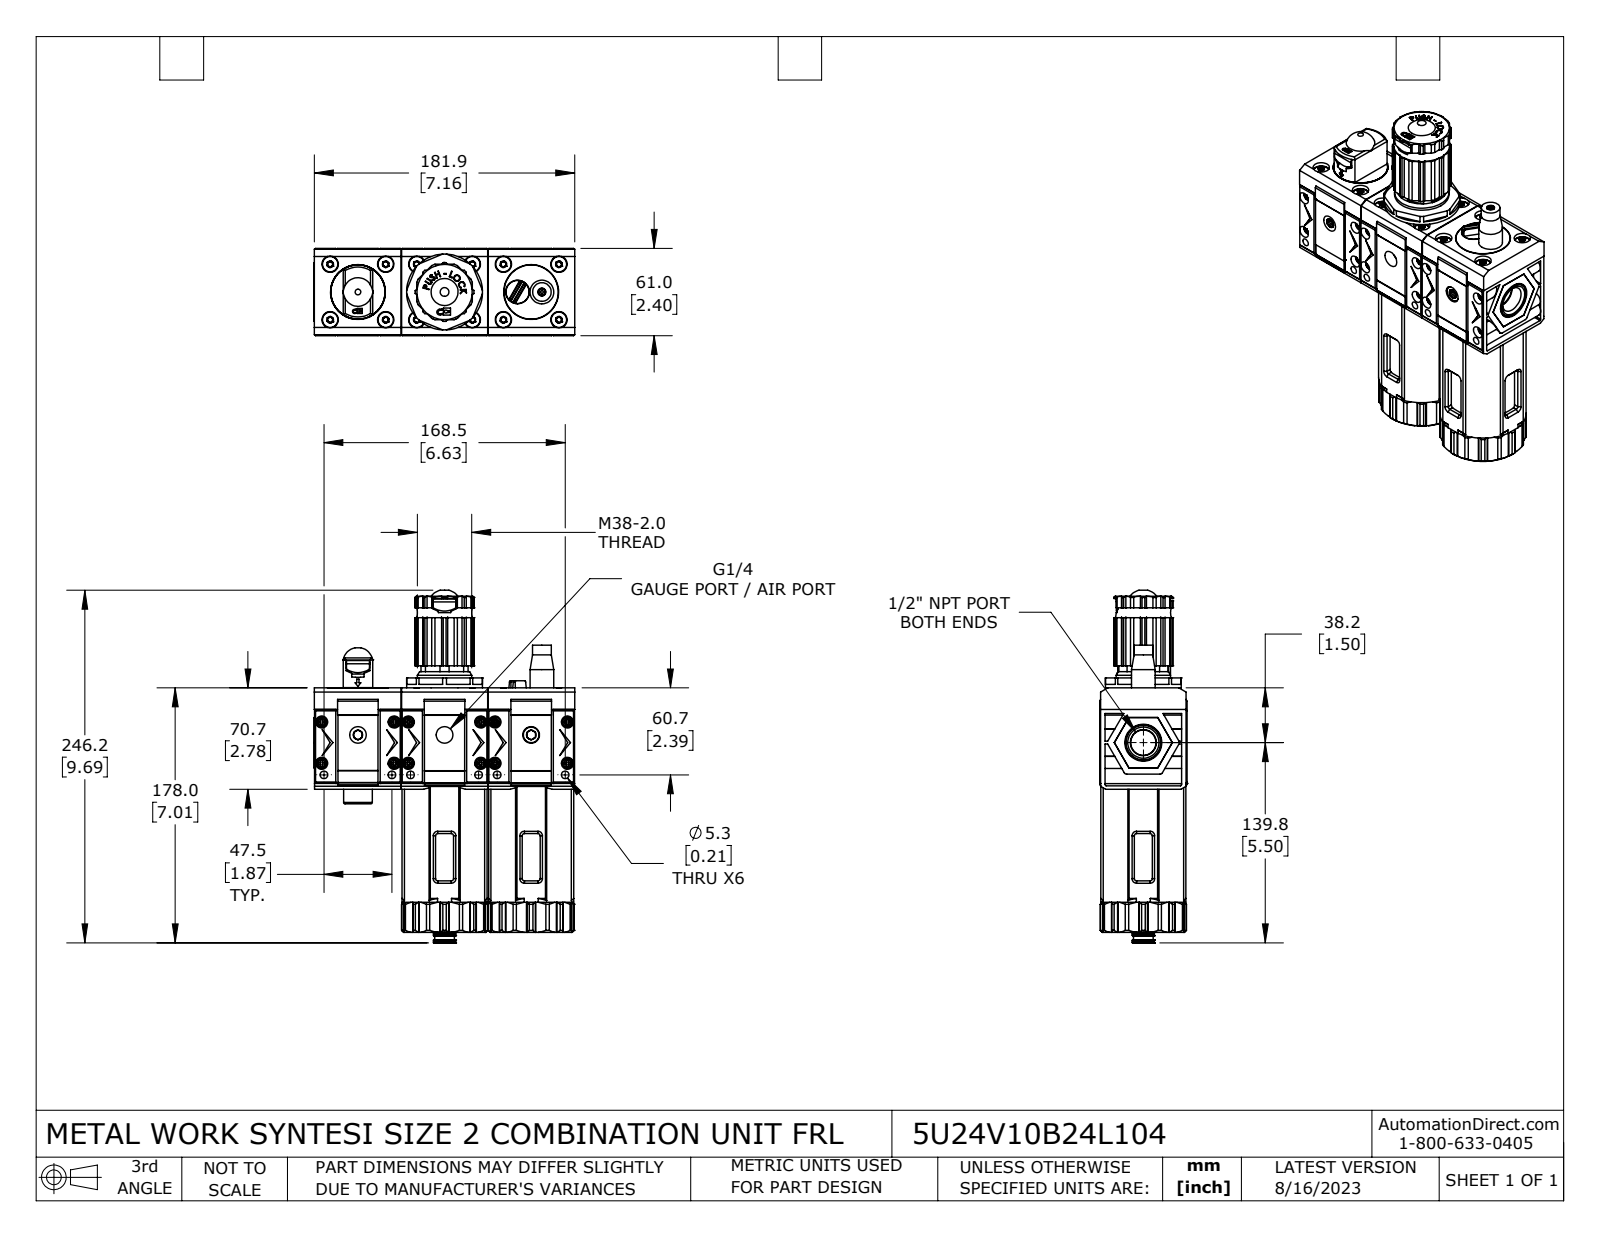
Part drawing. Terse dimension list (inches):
name: 5U24V10B24L104
written by: SolidWorks 2021 (CONFIG_CONTROL_DESIGN)
unit: in
bodies: 40 solids, 3750 faces (2199 planar, 1017 cylindrical, 534 other)
size: 9.693 × 7.173 × 2.402
volume: 68.23 in³; area: 503.7 in²
holes: 12× ⌀0.128, 12× ⌀0.165, 12× ⌀0.331, 12× ⌀0.449, 6× ⌀0.209, 3× ⌀0.457, 3× ⌀1.508, 2× ⌀1.929, 2× ⌀1.969, 2× ⌀2.008, 2× ⌀2.028, 1× ⌀0.126
bosses: 12× ⌀0.276, 12× ⌀0.189, 12× ⌀0.15, 2× ⌀1.496, 1× ⌀2.087, 1× ⌀1.488, 1× ⌀1.248, 1× ⌀1.035
rounds: 84× R0.011, 32× R0.02, 16× R0.059, 12× R0.069, 12× R0.191, 6× R0.242, 4× R0.807, 3× R0.12
face distances: 2.382, 2.39, 0.094, 2.193, 2.098, 2.402, 2.374, 3.11, 5.303, 3.205
hole spacings: 2.382, 1.08, 1.528, 4.764, 1.789, 2.638, 2.83, 3.237
